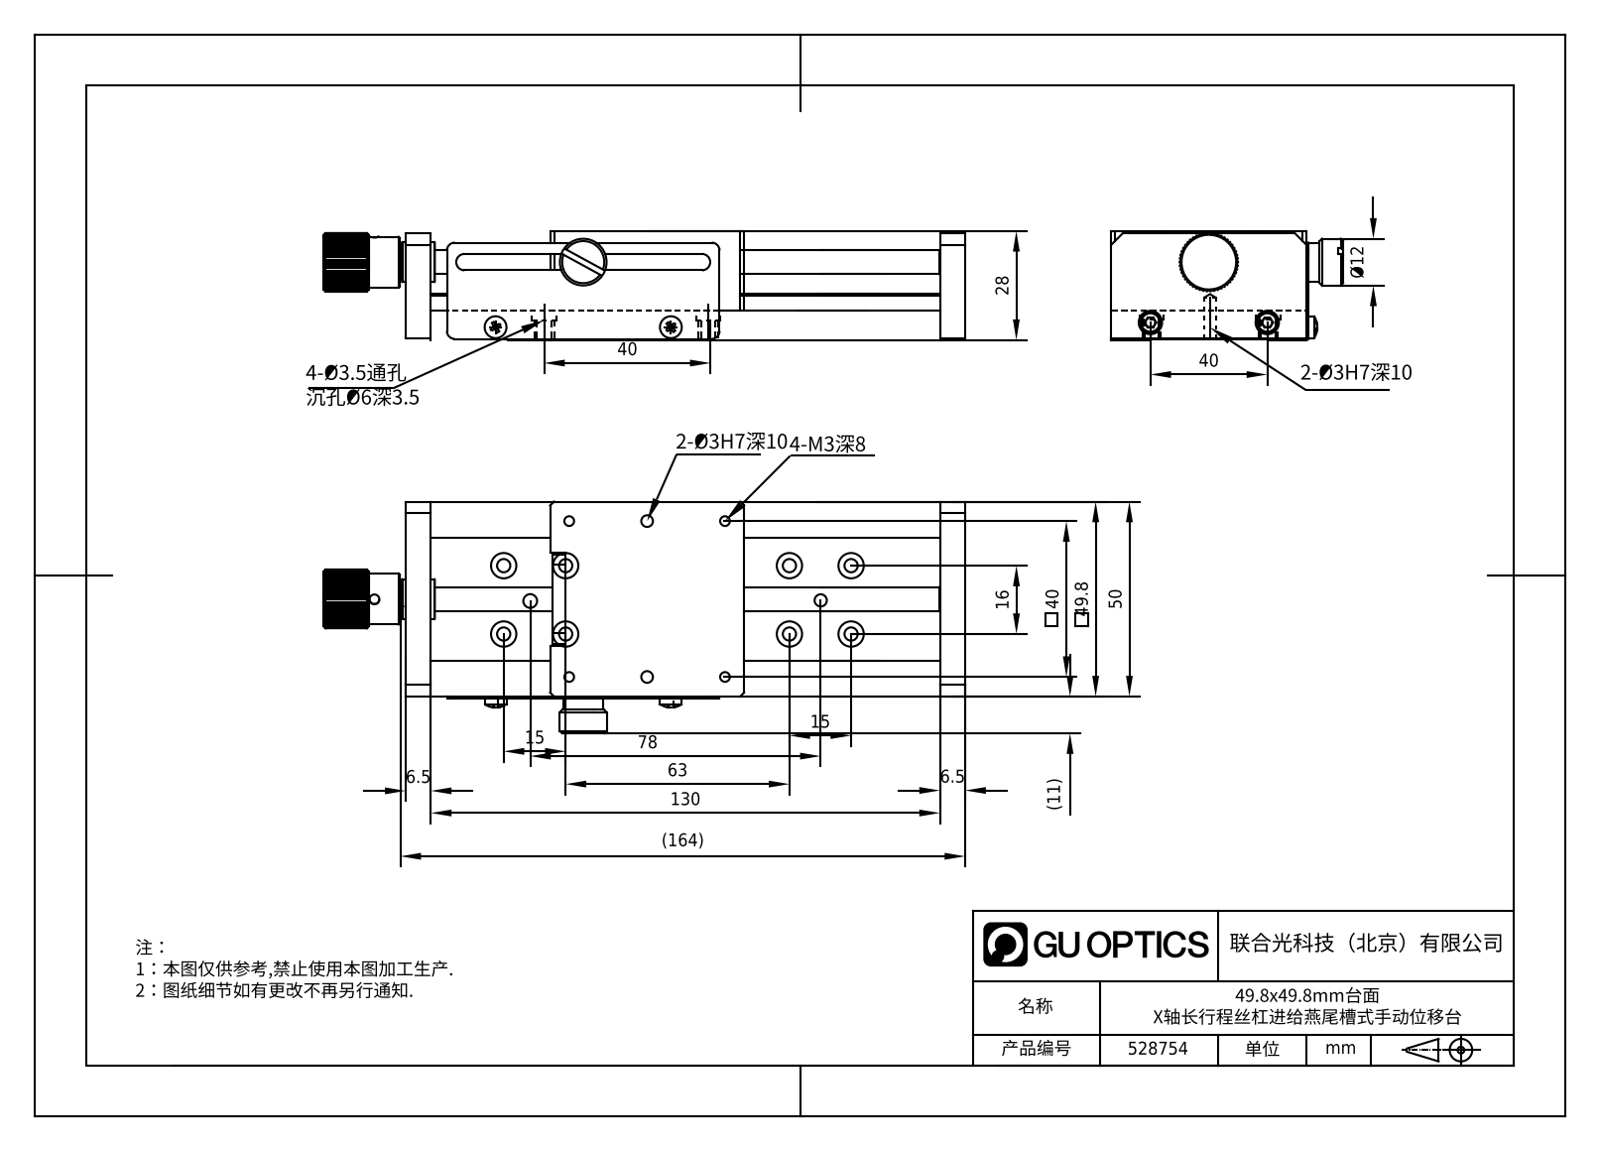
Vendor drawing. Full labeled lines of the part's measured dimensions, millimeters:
Part name (STEP PRODUCT): 528754
STEP written by: SolidWorks 2020 (CONFIG_CONTROL_DESIGN)
Units: millimetres
Bodies: 0 solids, 756 faces (375 planar, 196 cylindrical, 185 other)
Overall size (bounding box): 164 × 59.45 × 28
Round holes (diameter × count): ⌀3.4 ×14, ⌀2.5 ×12, ⌀6 ×11, ⌀2.05 ×6, ⌀3 ×5, ⌀2.9 ×4, ⌀5 ×4, ⌀6.5 ×4, ⌀1.5 ×2, ⌀3.1 ×2, ⌀3.3 ×1, ⌀3.5 ×1
Round bosses / shafts (diameter × count): ⌀4.5 ×4, ⌀3 ×4, ⌀2.5 ×4, ⌀5.6 ×2, ⌀5.5 ×2, ⌀13 ×1, ⌀12 ×1, ⌀10.3 ×1
Partial cylindrical surfaces — rounded edges, fillets, slot ends (radius × count): R0.3 ×8, R2 ×4, R2.1 ×2, R7.5 ×1, R11.5 ×1
Main face-to-face distances: 12, 4.5, 11.8, 7.3, 7.5, 27.8, 6.5, 136.5, 16, 20.5
Hole centre spacings: 10.97, 8.5, 15, 40, 78, 16, 16.62, 20
